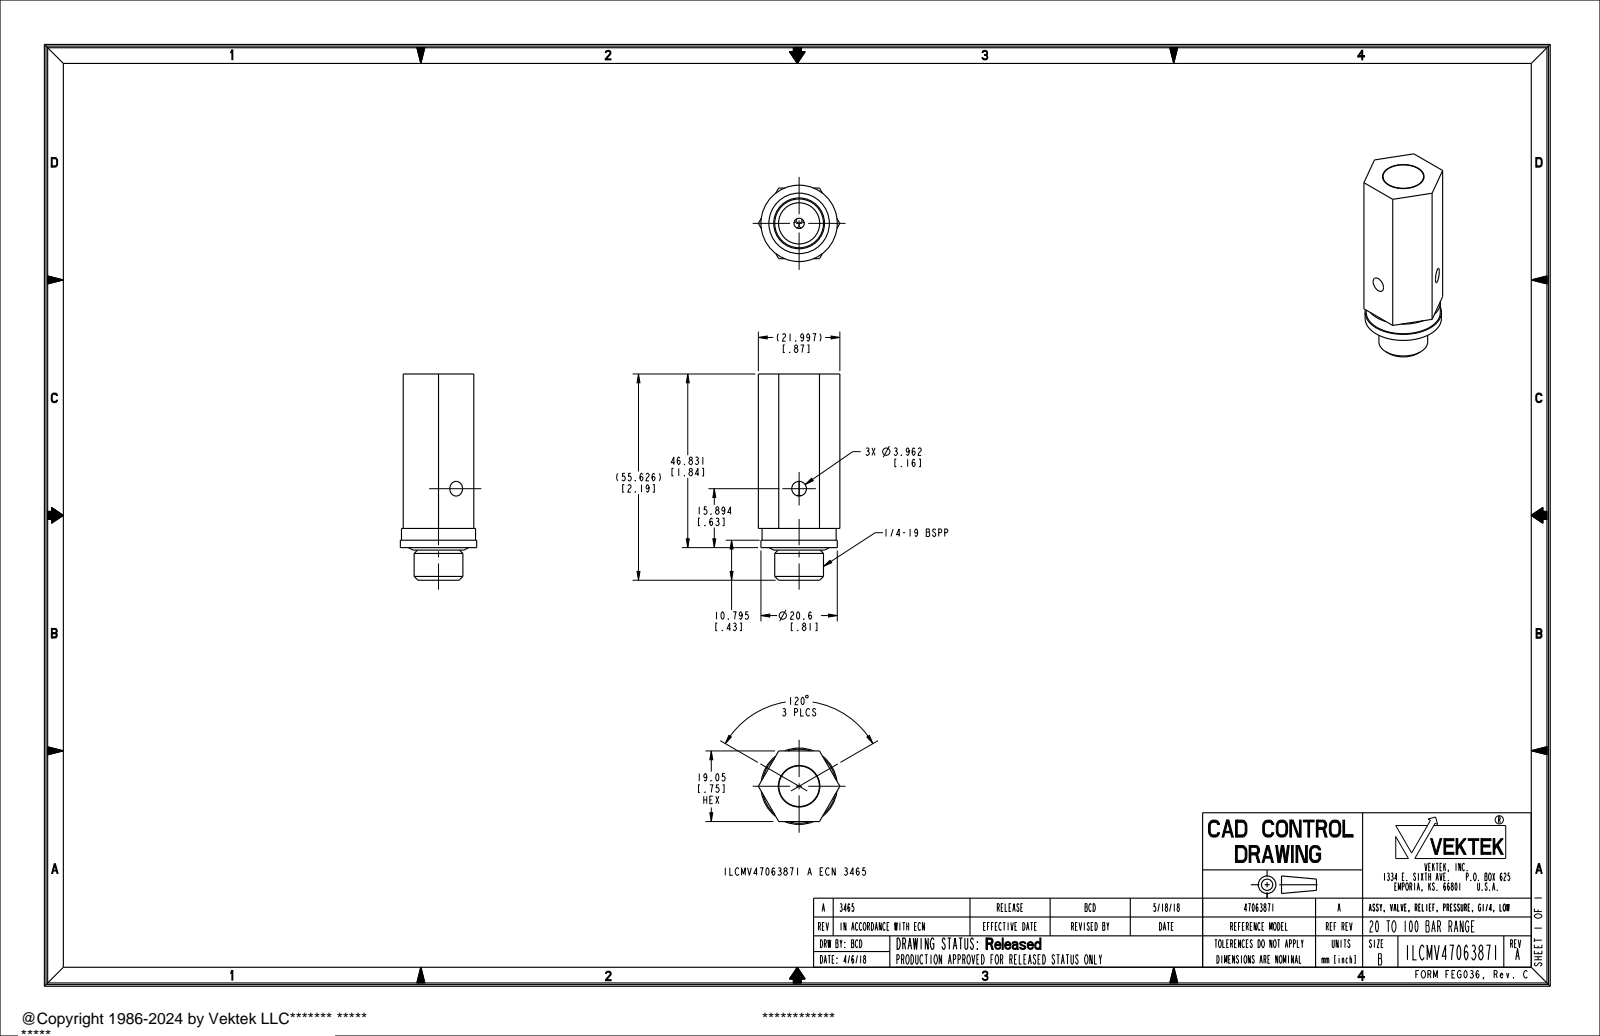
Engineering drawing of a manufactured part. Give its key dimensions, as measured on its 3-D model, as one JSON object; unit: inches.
{"part_name": "ILCMV47063871", "step_written_by": "PRO/ENGINEER BY PARAMETRIC TECHNOLOGY CORPORATION, 2013320 (AUTOMOTIVE_DESIGN)", "units": "inches", "bodies": {"solids": 1, "faces": 56, "planar": 28, "cylindrical": 22, "other": 6}, "overall_size": [2.19, 0.866, 0.811], "volume_in3": 0.935, "surface_area_in2": 7.671, "round_holes": [[0.156, 3], [0.109, 1], [0.441, 1], [0.539, 1]], "round_bosses_or_shafts": [[0.811, 1], [0.787, 1], [0.518, 1], [0.437, 1], [0.431, 1]], "face_to_face_distances": [0.75, 0.75, 1.844, 0.346, 2.19, 0.425, 0.079, 1.765, 0.55, 0.204]}
